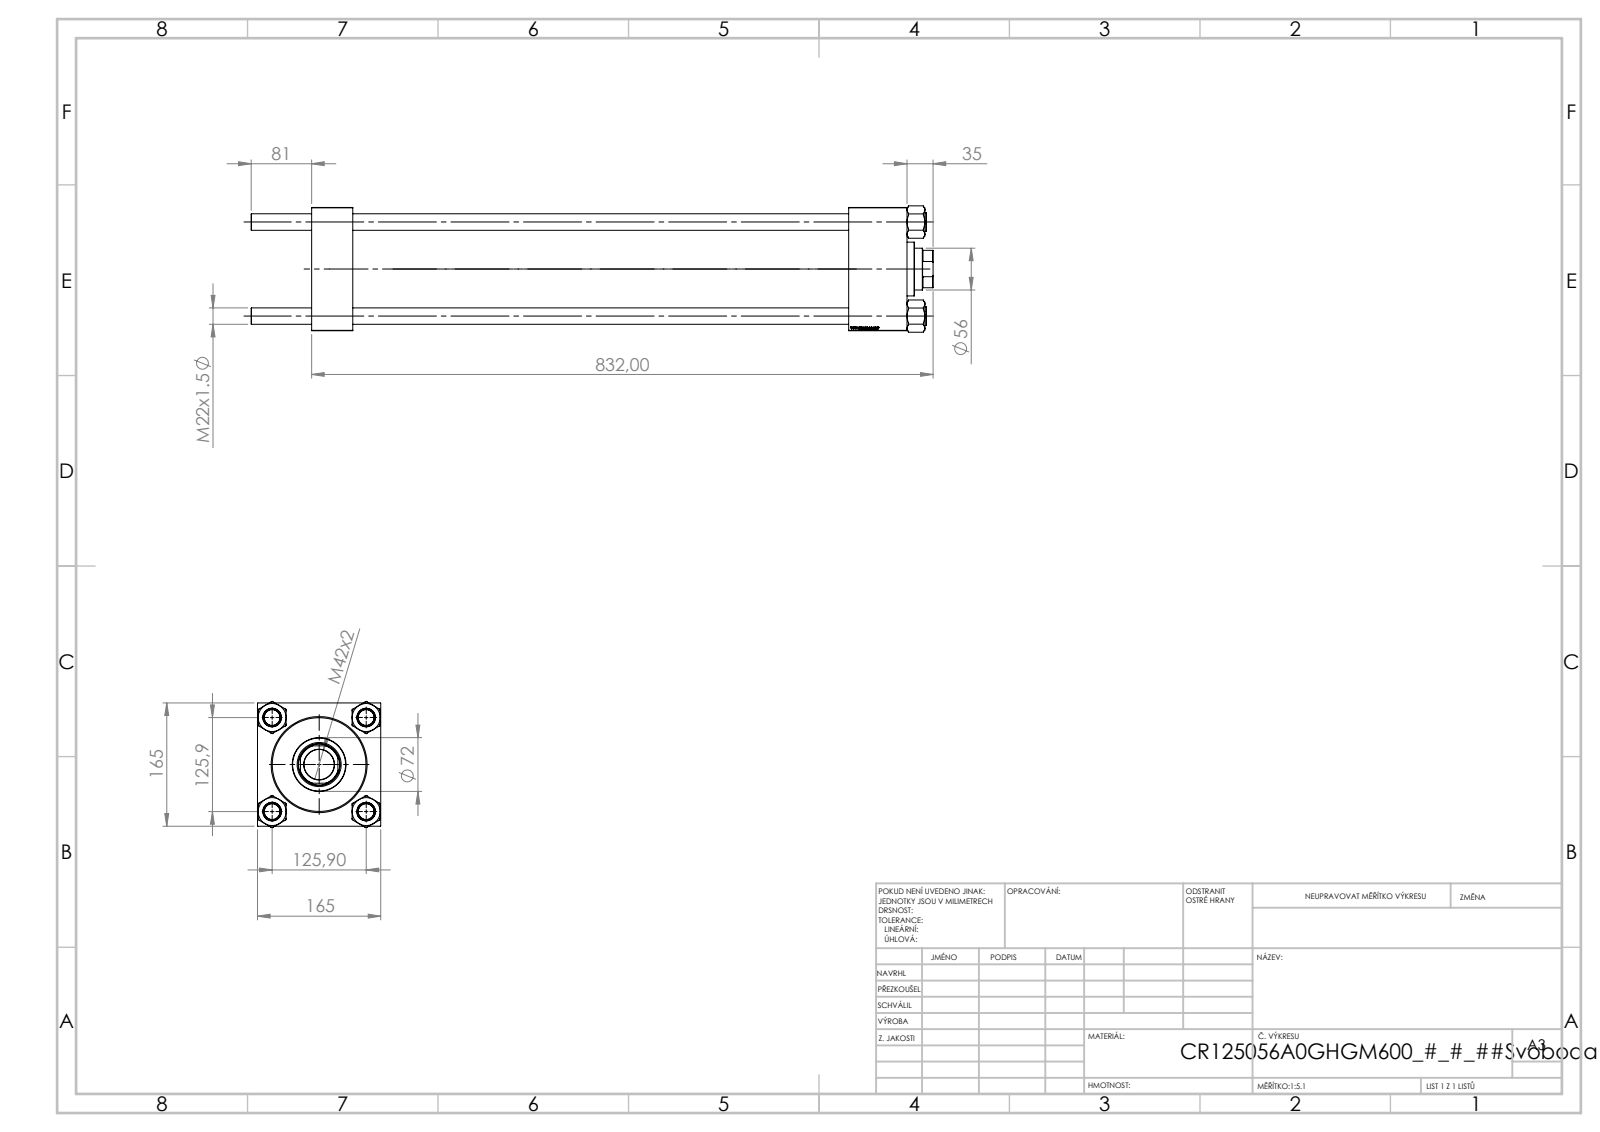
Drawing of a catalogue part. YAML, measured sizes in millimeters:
part_name: "NUT_M5; V215CR_VCP; CR025_012_A_0_G_A_G_M_020_+#_##_TYCINKA; V215_VC_A (+1 more)"
step_written_by: "SolidWorks 2019 (CONFIG_CONTROL_DESIGN)"
units: millimeters
bodies: {solids: 11, faces: 1182, planar: 568, cylindrical: 78, other: 536}
overall_size: [913, 169.14, 165]
volume: 7691000
surface_area: 1277000
round_holes:
  - {diameter: 22, count: 4}
  - {diameter: 7, count: 2}
  - {diameter: 32.24, count: 2}
  - {diameter: 45, count: 2}
  - {diameter: 40.5, count: 1}
  - {diameter: 56, count: 1}
  - {diameter: 59, count: 1}
  - {diameter: 96, count: 1}
  - {diameter: 125, count: 1}
  - {diameter: 125.5, count: 1}
round_bosses_or_shafts:
  - {diameter: 25, count: 4}
  - {diameter: 131, count: 1}
  - {diameter: 72, count: 1}
partial_cylinders:
  - {radius: 27, count: 1}
face_to_face_distances: [165, 55, 797, 742, 719, 664, 78, 768.3, 713.3, 49.3]
hole_center_spacings: [89.02, 125.9, 178.05, 718.5]
